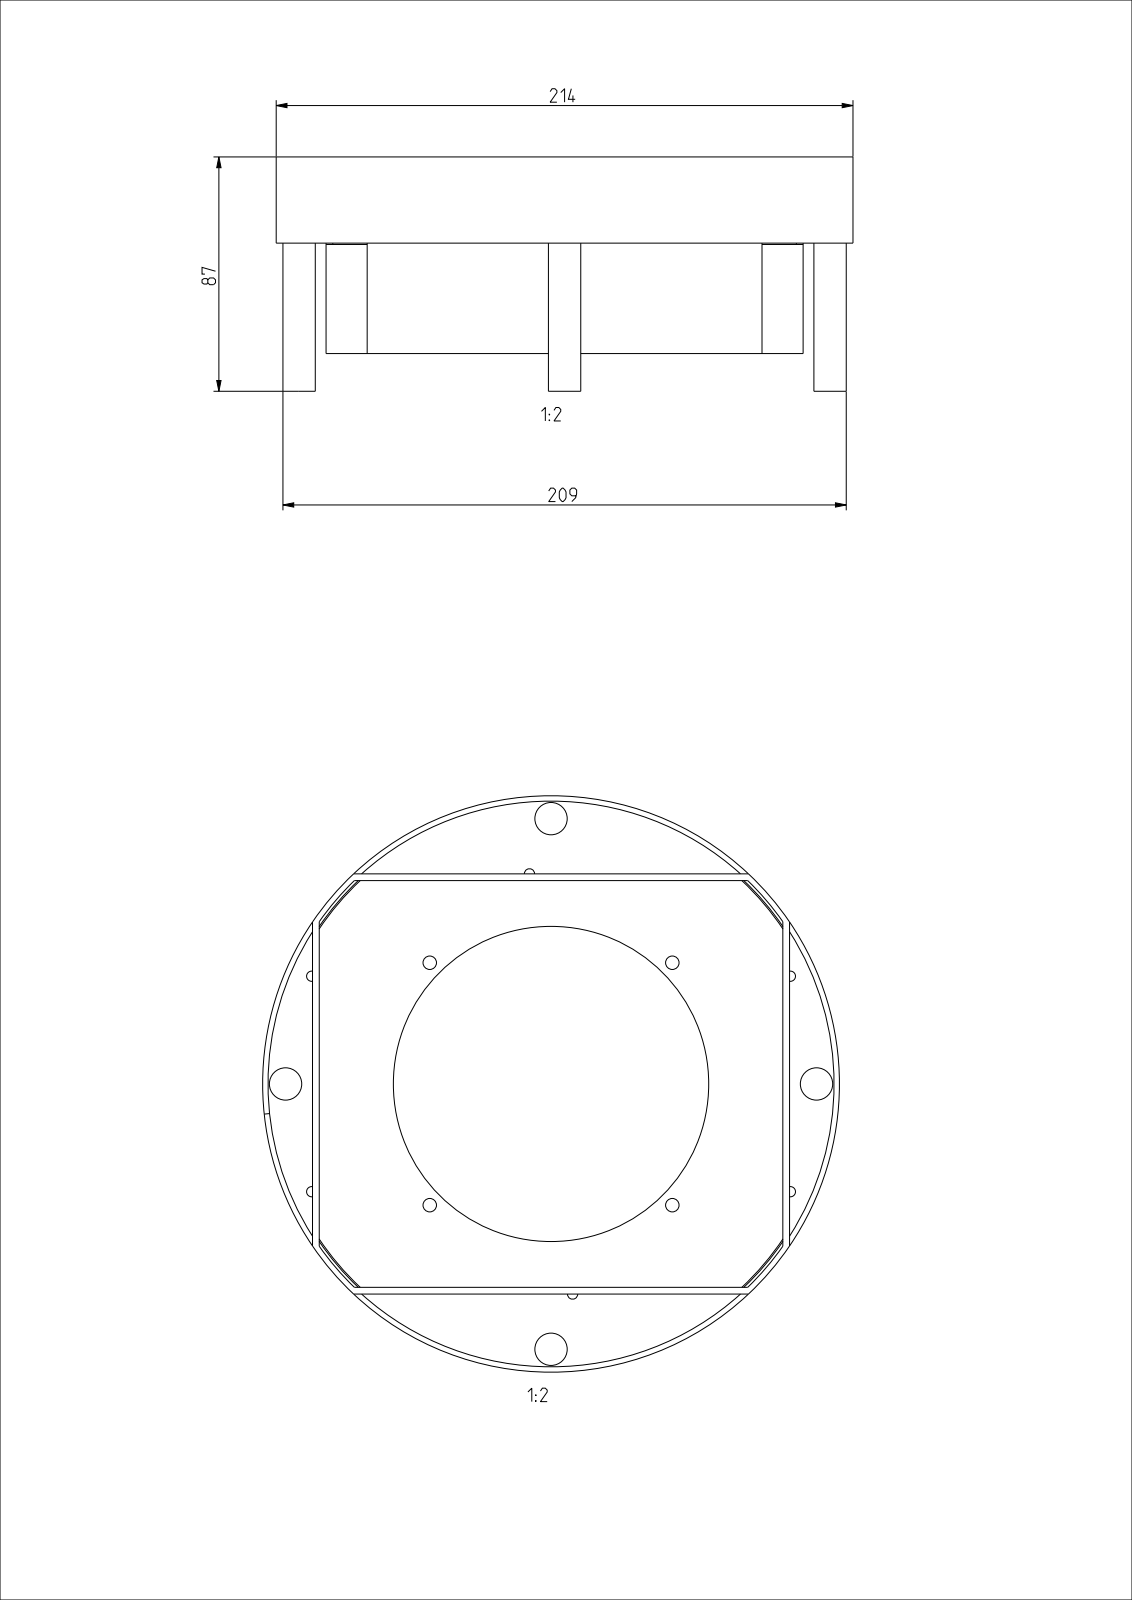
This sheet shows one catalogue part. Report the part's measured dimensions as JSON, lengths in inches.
{"part_name": "T-00671; T-00672; T-00673; T-00675 (+8 more)", "step_written_by": "CREO PARAMETRIC BY PTC INC, 2022024 (AUTOMOTIVE_DESIGN)", "units": "inches", "bodies": {"solids": 9, "faces": 169, "planar": 97, "cylindrical": 72, "other": 0}, "overall_size": [8.425, 8.425, 3.425], "volume_in3": 26.68, "surface_area_in2": 470.5, "round_holes": [[0.15, 6], [0.197, 4], [0.398, 4], [4.606, 1], [8.268, 1]], "round_bosses_or_shafts": [[0.472, 4], [0.388, 4], [8.425, 1], [8.189, 1], [8.15, 1], [8.031, 1]], "partial_cylinders_radius": [[0.02, 8]], "face_to_face_distances": [0.079, 0.098, 0.591, 0.472, 0.394, 6.87, 0.669, 6.043, 0.197, 0.118], "hole_center_spacings": [2.752, 5.921, 1.62, 1.735, 2.506, 3.543, 3.765, 3.834]}
